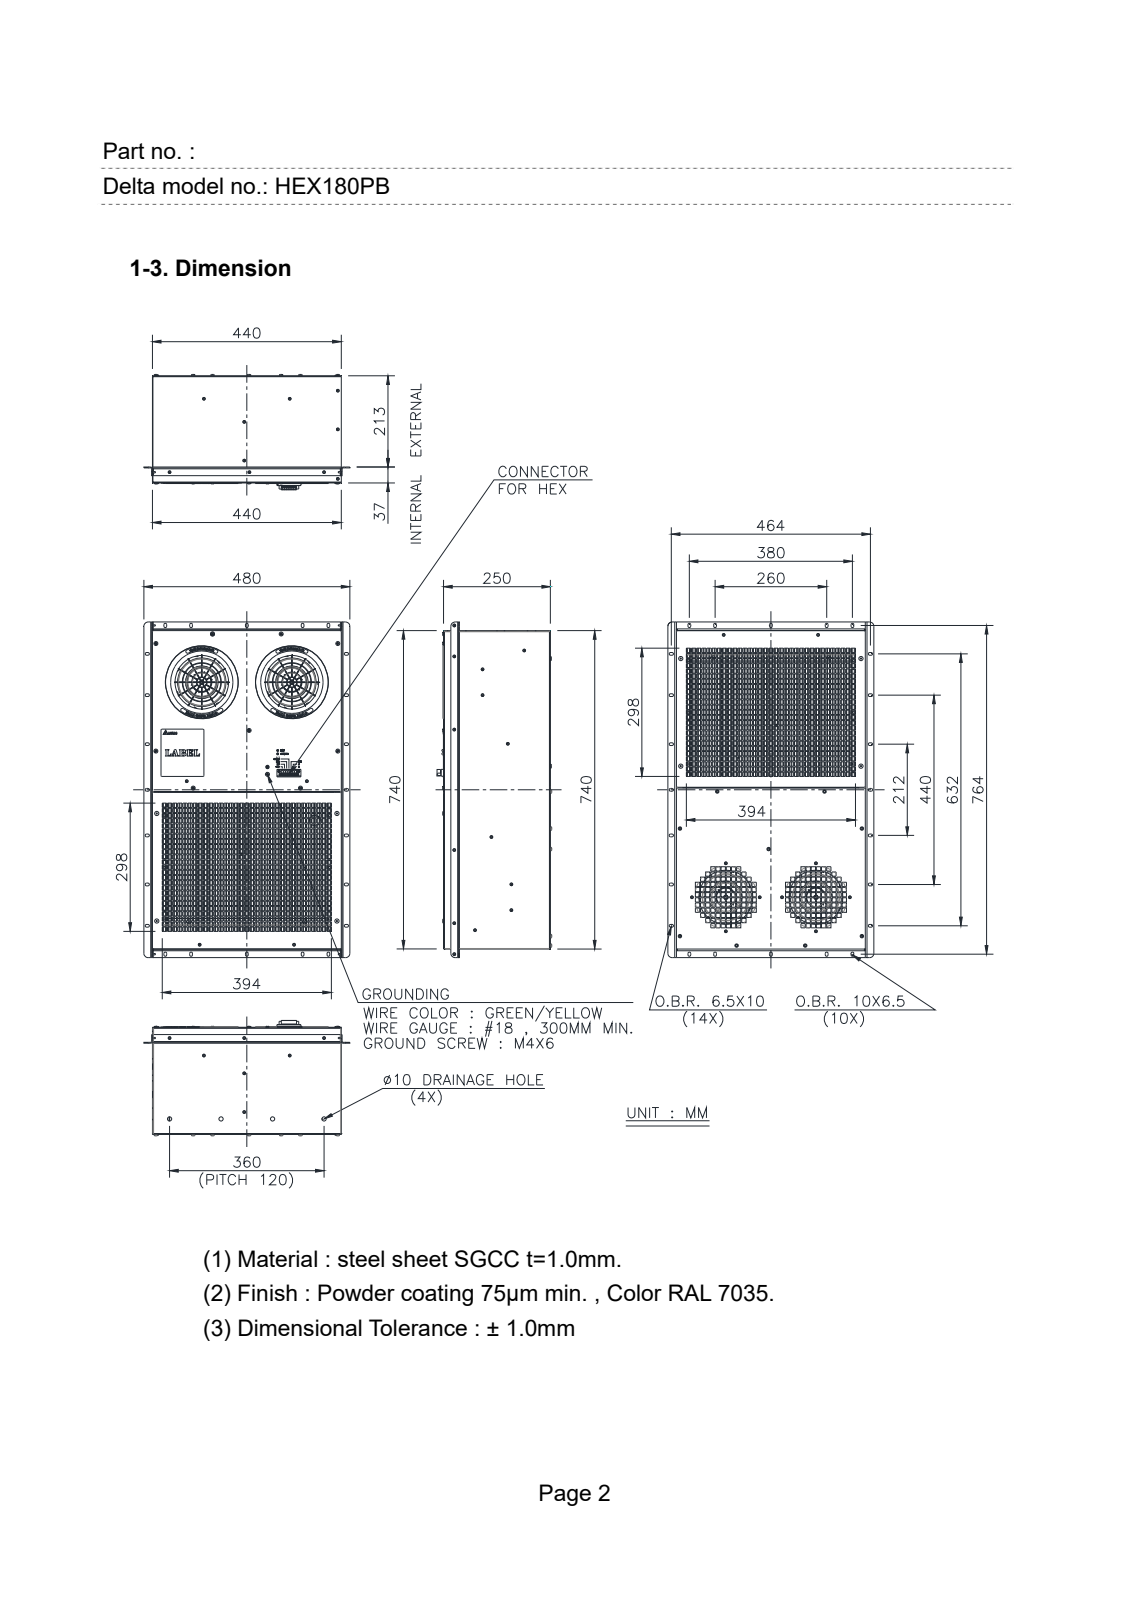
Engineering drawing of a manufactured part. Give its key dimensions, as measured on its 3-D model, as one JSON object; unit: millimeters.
{"part_name": "HEX180PB", "step_written_by": "CREO PARAMETRIC BY PTC INC, 2015080 (CONFIG_CONTROL_DESIGN)", "units": "millimeters", "bodies": {"solids": 1, "faces": 9642, "planar": 9550, "cylindrical": 92, "other": 0}, "overall_size": [780, 480, 264], "volume_mm3": 80810000, "surface_area_mm2": 1502000, "round_holes": [[10, 4], [150, 2]], "round_bosses_or_shafts": [[170, 2], [5, 2], [8, 1]], "partial_cylinders_radius": [[3.25, 48], [10, 6]], "face_to_face_distances": [2, 249, 247, 440, 740, 35, 212, 245, 37, 210], "hole_center_spacings": [120, 240, 210, 360]}
